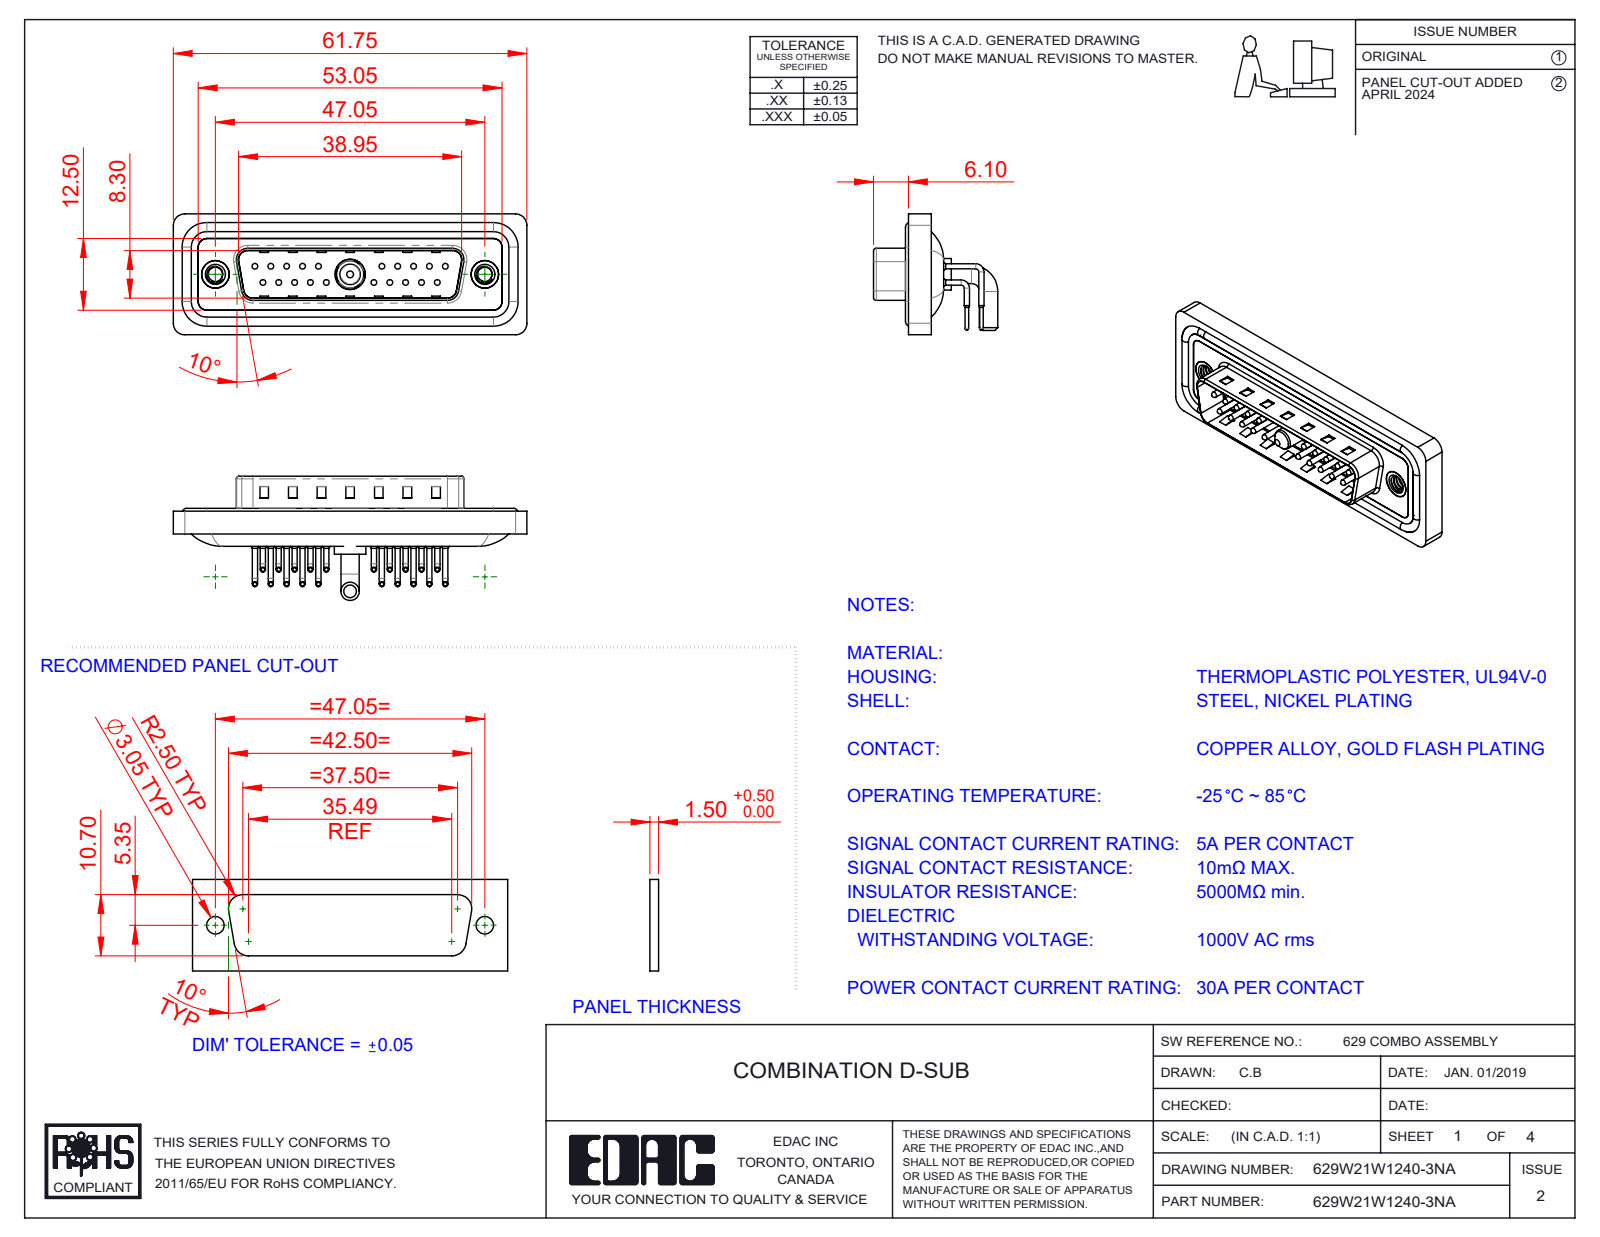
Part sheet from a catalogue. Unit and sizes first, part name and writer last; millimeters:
Units: millimetres
Overall size (bounding box): 61.75 × 21.7 × 21.1
Round holes (diameter × count): ⌀0.75 ×20, ⌀1.6 ×20, ⌀2 ×20, ⌀2.5 ×2, ⌀4 ×2, ⌀4.8 ×2, ⌀5 ×2, ⌀4.85 ×1, ⌀5.3 ×1
Round bosses / shafts (diameter × count): ⌀0.9 ×40, ⌀1.5 ×20, ⌀1 ×20, ⌀0.65 ×20, ⌀1.6 ×4, ⌀4.9 ×2, ⌀3.2 ×2, ⌀5.5 ×1
Partial cylindrical surfaces — rounded edges, fillets, slot ends (radius × count): R1.01 ×20, R1.5 ×18, R2 ×18, R0.5 ×8, R1.6 ×8, R0.25 ×4, R0.6 ×4, R0.65 ×4
Main face-to-face distances: 0.4, 2.9, 0.8, 4.1, 1.1, 2.1, 1.6, 4.5, 1.5, 2.5
Hole centre spacings: 3.16, 2.77, 5.54, 8.31, 5.04, 19.39, 20.97, 22.16
Volume: 7 450 mm³ · Surface area: 12 743 mm²
Bodies: 29 solids, 2720 faces (1499 planar, 927 cylindrical, 294 other)
Part name (STEP PRODUCT): 629Combo Housing_21W1; 629Combo Threaded Rivet_A; 629Combo Shell Front_25 Contacts; Power Pin_30A RA (+5 more)
STEP written by: SolidWorks 2023 (CONFIG_CONTROL_DESIGN)
